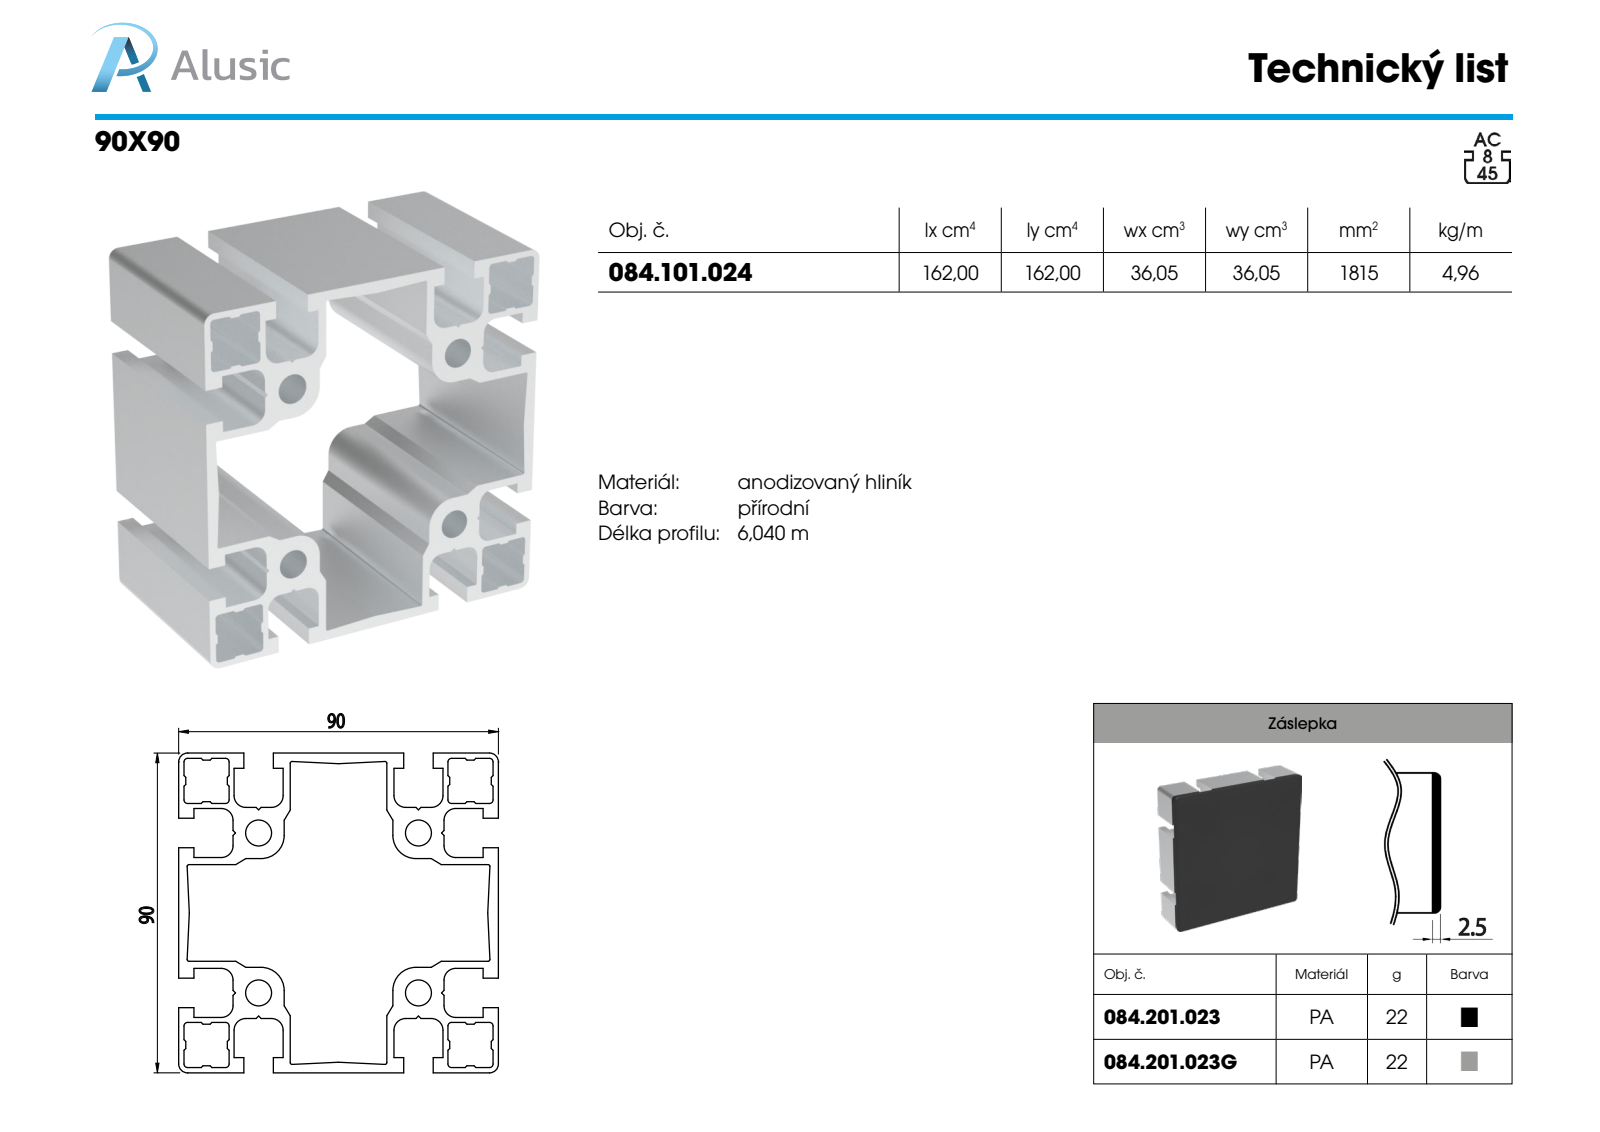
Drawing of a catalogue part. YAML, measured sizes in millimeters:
part_name: "084.101.024"
step_written_by: "SolidWorks 2018 (AUTOMOTIVE_DESIGN)"
units: millimeters
bodies: {solids: 1, faces: 176, planar: 122, cylindrical: 54, other: 0}
overall_size: [100, 90, 90]
volume: 186951
surface_area: 129706
round_holes:
  - {diameter: 7.3, count: 4}
partial_cylinders:
  - {radius: 1, count: 20}
  - {radius: 3, count: 16}
  - {radius: 2.5, count: 4}
  - {radius: 3.2, count: 4}
face_to_face_distances: [90, 58.6, 14.1, 45, 2, 29.4, 88, 29.7, 60.3, 27.7]
hole_center_spacings: [45, 63.64]
